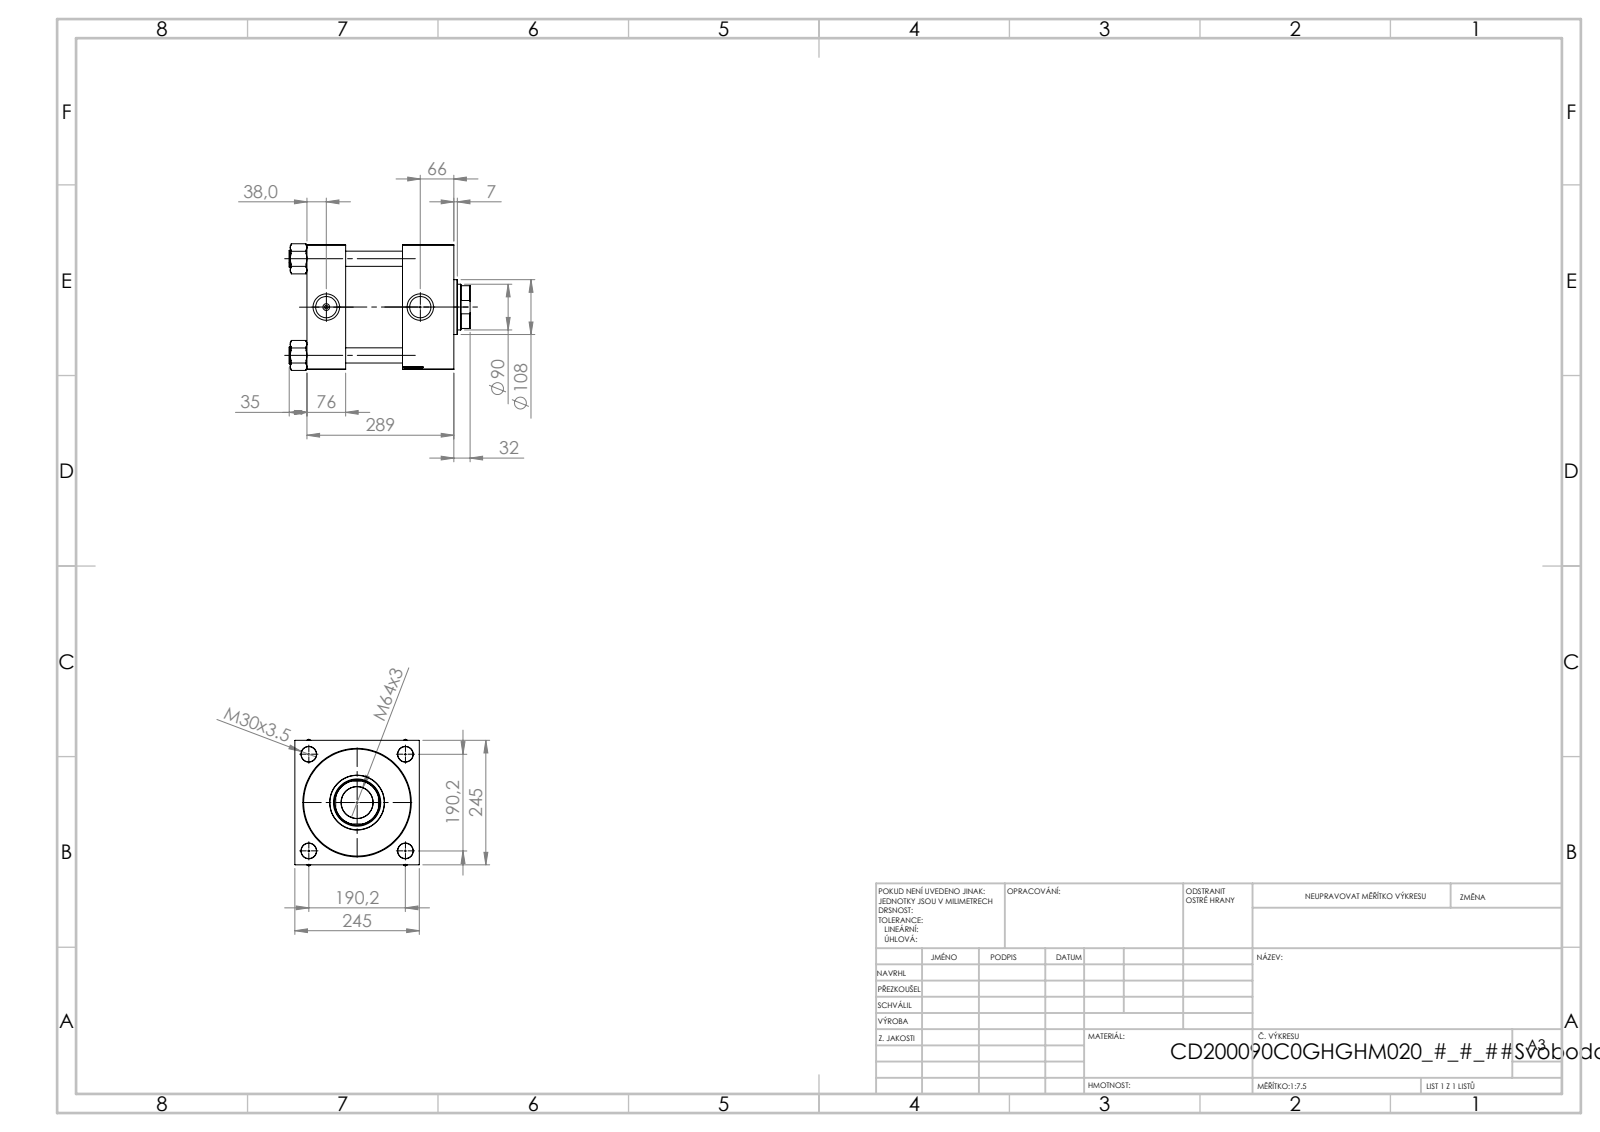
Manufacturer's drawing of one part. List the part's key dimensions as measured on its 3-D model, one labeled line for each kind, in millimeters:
Part name (STEP PRODUCT): V215CD_Body_C; V215CD_VCP_C; NUT_M5_V215CD_C; V215CD_VC_C (+1 more)
STEP written by: SolidWorks 2019 (CONFIG_CONTROL_DESIGN)
Units: millimetres
Bodies: 11 solids, 1196 faces (574 planar, 86 cylindrical, 536 other)
Overall size (bounding box): 356 × 249.44 × 245
Volume: 13 440 000 mm³ · Surface area: 1 039 000 mm²
Round holes (diameter × count): ⌀30 ×4, ⌀7 ×2, ⌀41.92 ×2, ⌀52 ×2, ⌀62.5 ×1, ⌀90 ×1, ⌀93 ×1, ⌀146 ×1, ⌀200 ×1, ⌀210.5 ×1
Round bosses / shafts (diameter × count): ⌀33 ×4, ⌀206 ×1, ⌀108 ×1
Partial cylindrical surfaces — rounded edges, fillets, slot ends (radius × count): R44 ×1
Main face-to-face distances: 245, 76, 289, 213, 260.3, 184.3, 28.7, 188, 112, 72.3
Hole centre spacings: 134.49, 190.2, 268.98, 185
